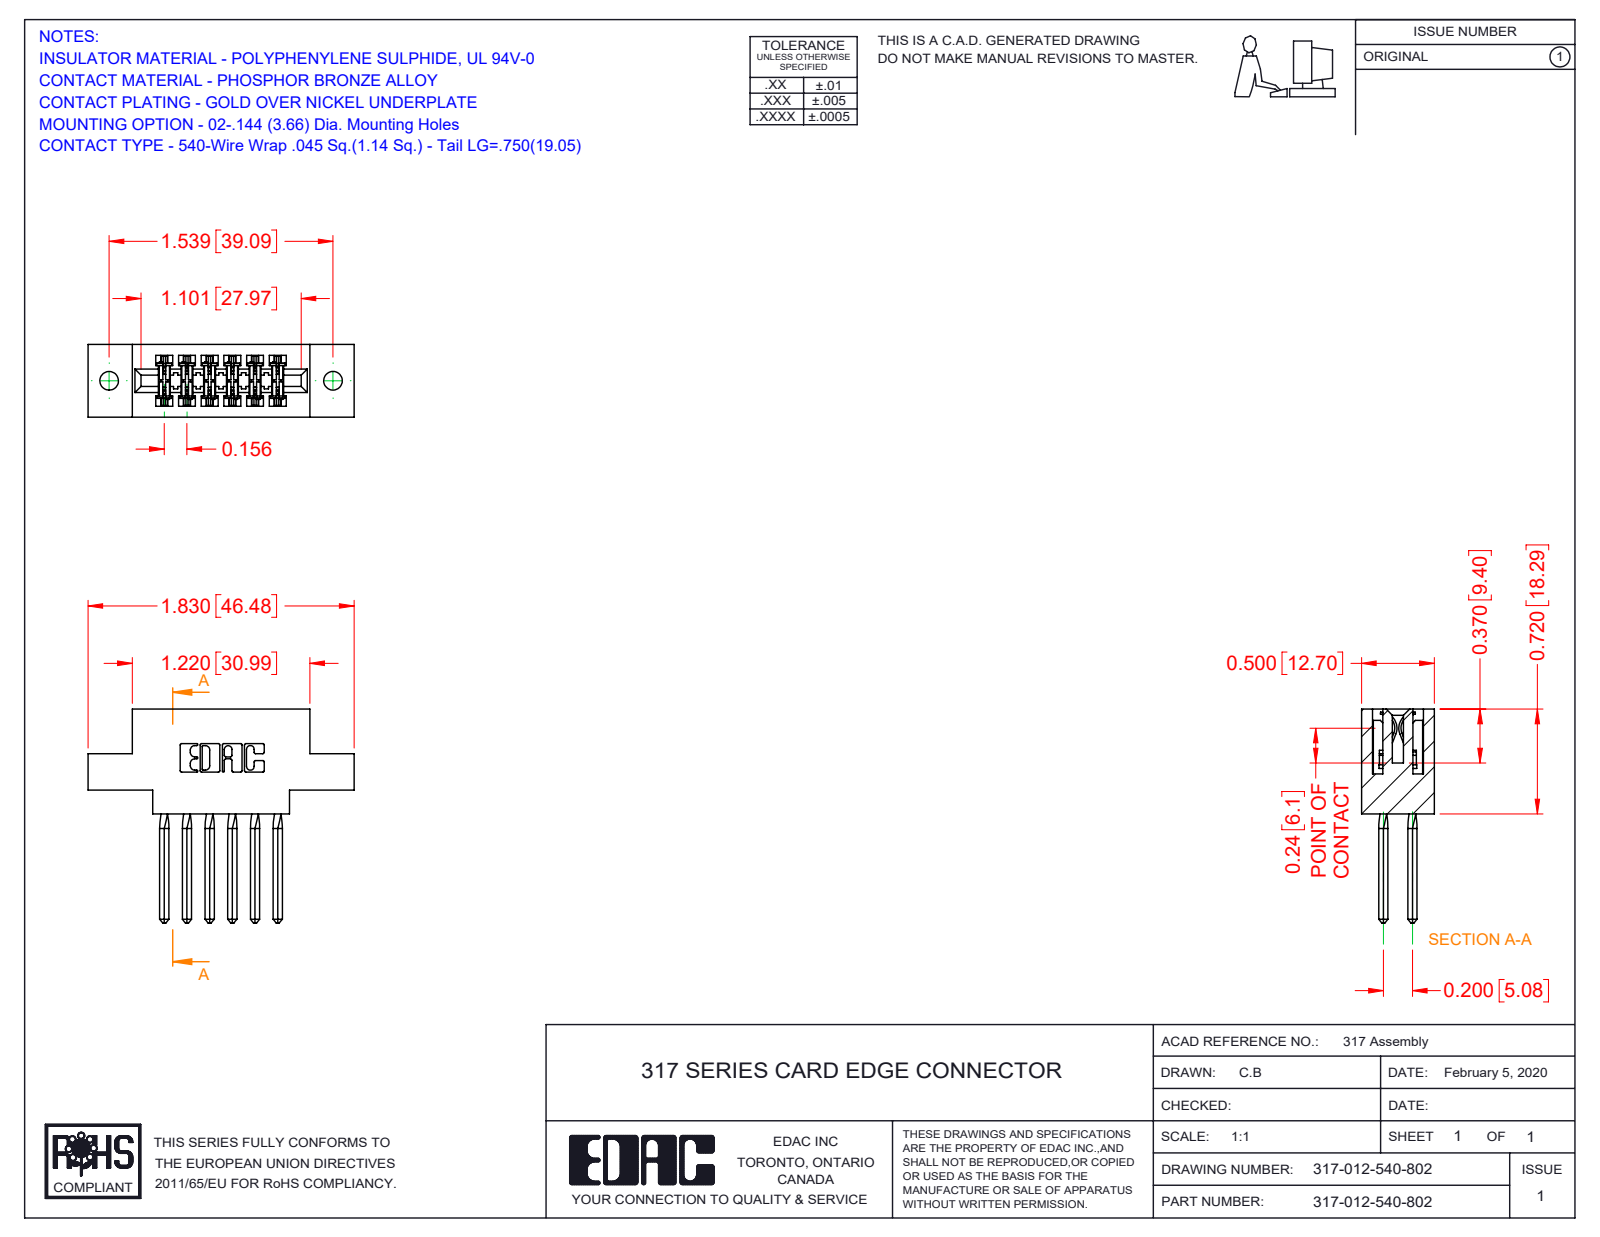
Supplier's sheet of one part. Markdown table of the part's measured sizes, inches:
| quantity | value |
| --- | --- |
| part name | 317-012-540-802; 317 Part_.144 Dia; 317-290-001_540 |
| STEP written by | SolidWorks 2016 (CONFIG_CONTROL_DESIGN) |
| units | inches |
| bodies | 13 solids, 1170 faces (934 planar, 188 cylindrical, 48 other) |
| overall size | 1.83 × 1.47 × 0.5 |
| volume | 0.4 in³ |
| surface area | 12.61 in² |
| round holes (diameter × count) | 0.128 × 2 |
| partial cylindrical surfaces (radius × count) | 0.015 × 24, 0.01 × 22, 0.007 × 6, 0.031 × 6, 0.026 × 3, 0.095 × 2, 0.1 × 2, 0.11 × 2 |
| main face-to-face distances | 0.5, 0.11, 0.075, 0.425, 0.22, 0.065, 0.156, 0.116, 0.163, 0.331 |
| hole center spacings | 1.539 |
